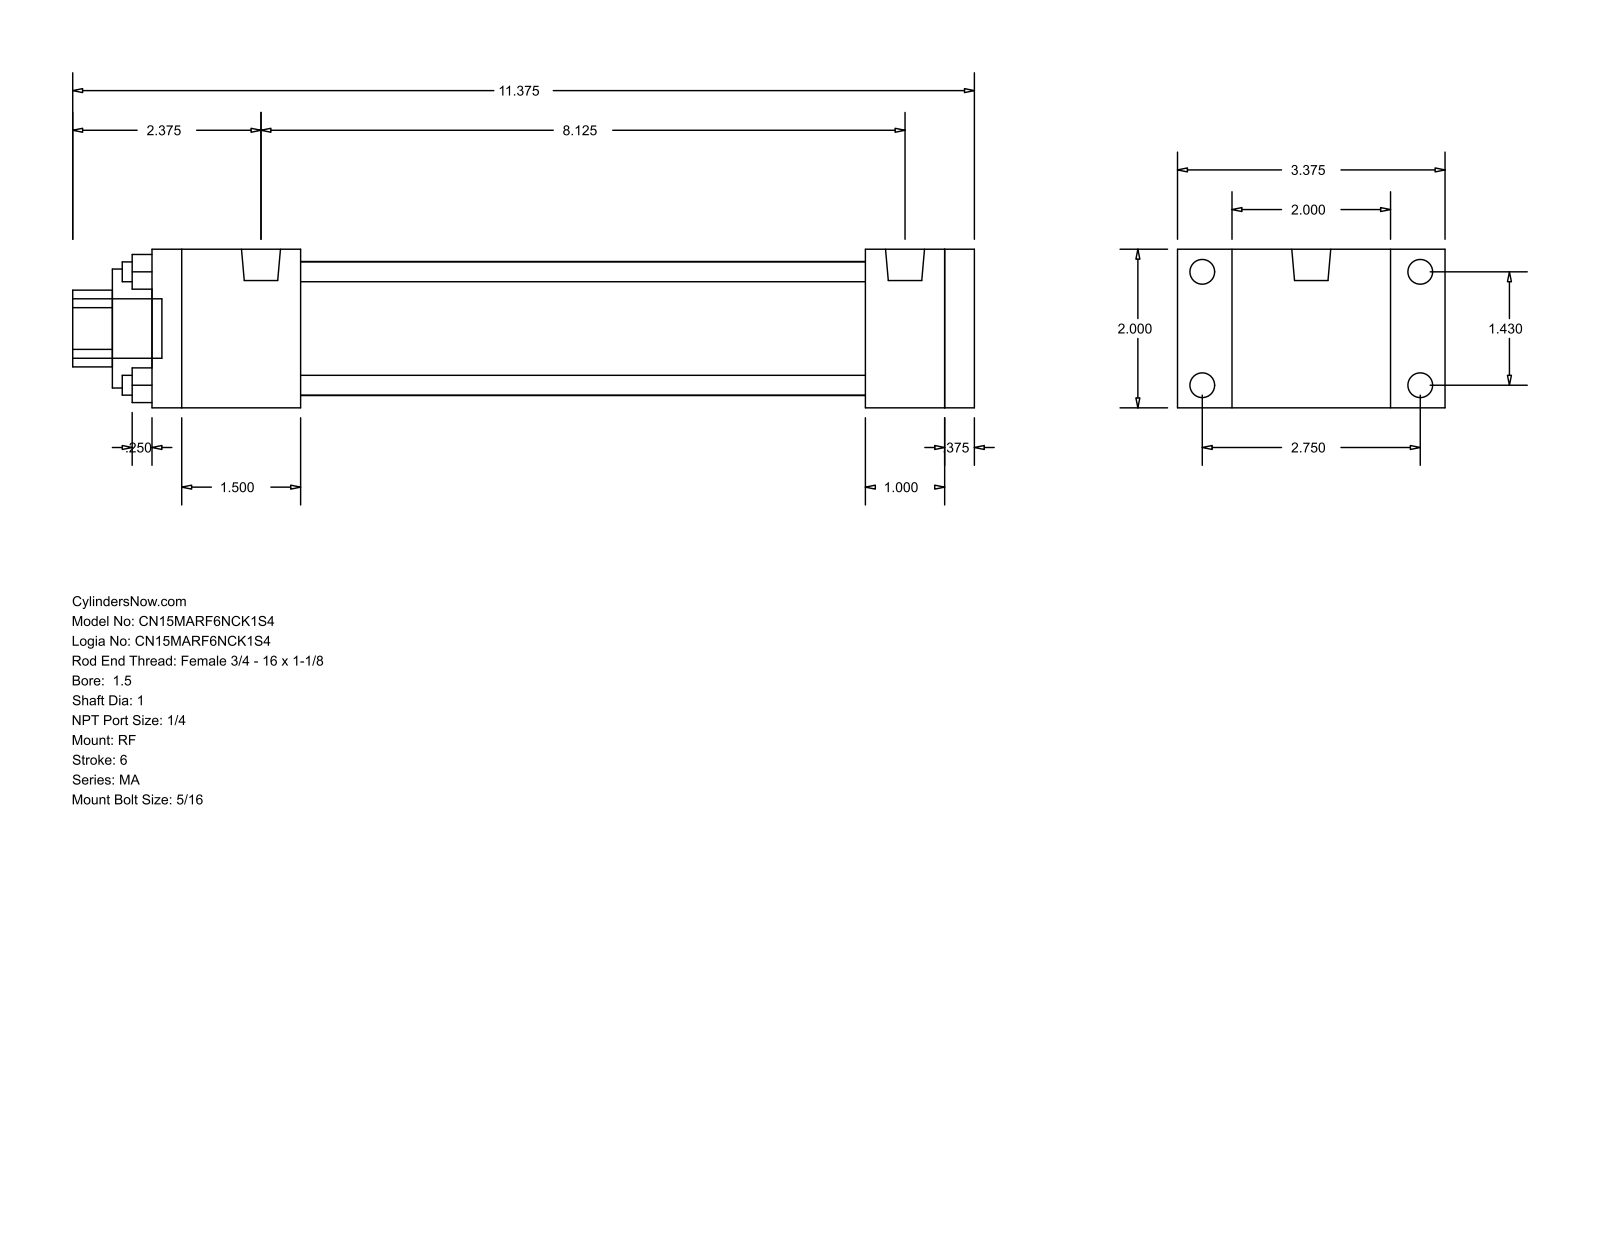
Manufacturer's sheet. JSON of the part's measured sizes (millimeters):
{"part_name": "MA_RF__0150_1", "step_written_by": "GSSL Pune (CONFIG_CONTROL_DESIGN)", "units": "millimeters", "bodies": {"solids": 0, "faces": 92, "planar": 64, "cylindrical": 28, "other": 0}, "overall_size": [288.93, 85.72, 50.8], "round_holes": [[6.35, 4], [25.4, 1], [38.1, 1], [42.93, 1]], "round_bosses_or_shafts": [[7.94, 8], [12.49, 2], [19.05, 1]], "partial_cylinders_radius": [[12.29, 1]], "face_to_face_distances": [50.8, 9.53, 254, 25.4, 263.53, 228.6, 34.93, 47.63, 180.97, 206.37], "hole_center_spacings": [25.68, 36.32, 51.36]}
